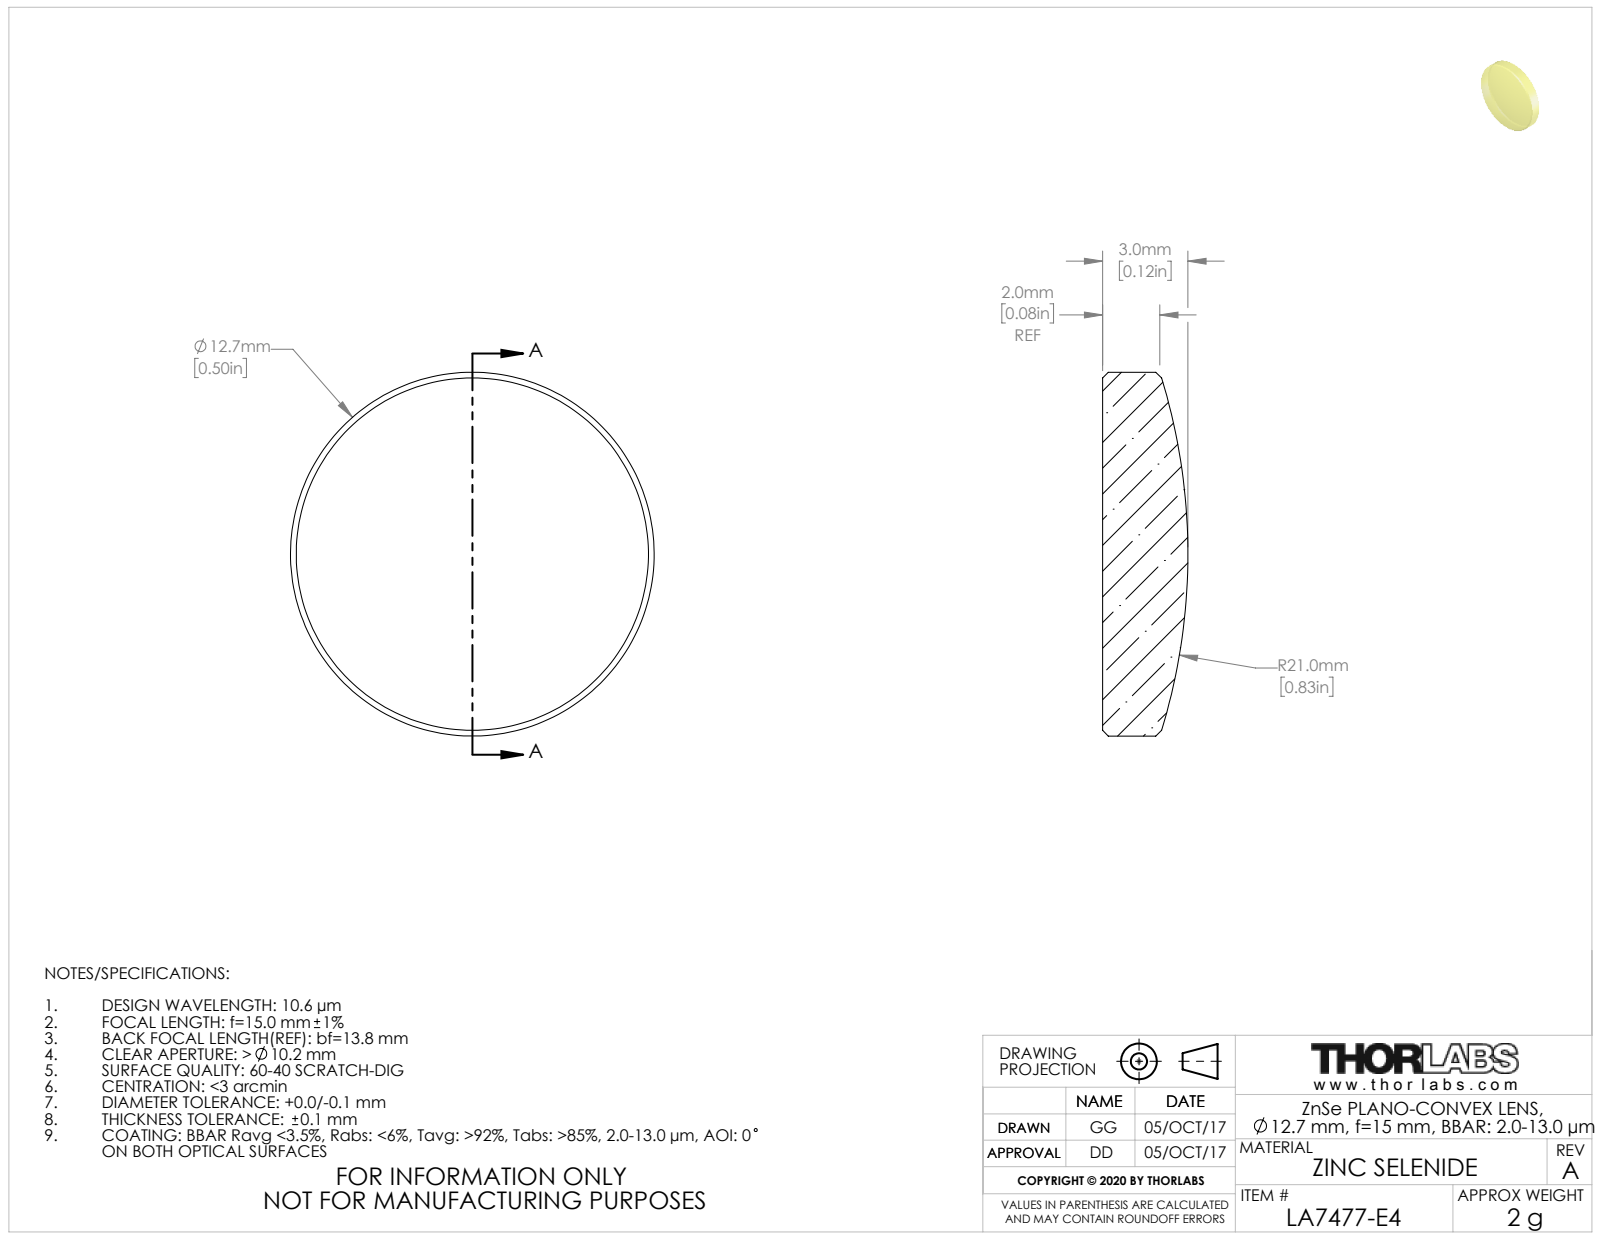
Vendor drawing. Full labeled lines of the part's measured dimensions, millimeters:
Part name (STEP PRODUCT): TTN097749-E0W
STEP written by: SolidWorks 2018 (CONFIG_CONTROL_DESIGN)
Units: millimetres
Bodies: 1 solid, 9 faces (1 planar, 2 cylindrical, 6 other)
Overall size (bounding box): 12.7 × 12.7 × 2.98
Volume: 315 mm³ · Surface area: 329 mm²
Round bosses / shafts (diameter × count): ⌀12.7 ×1
